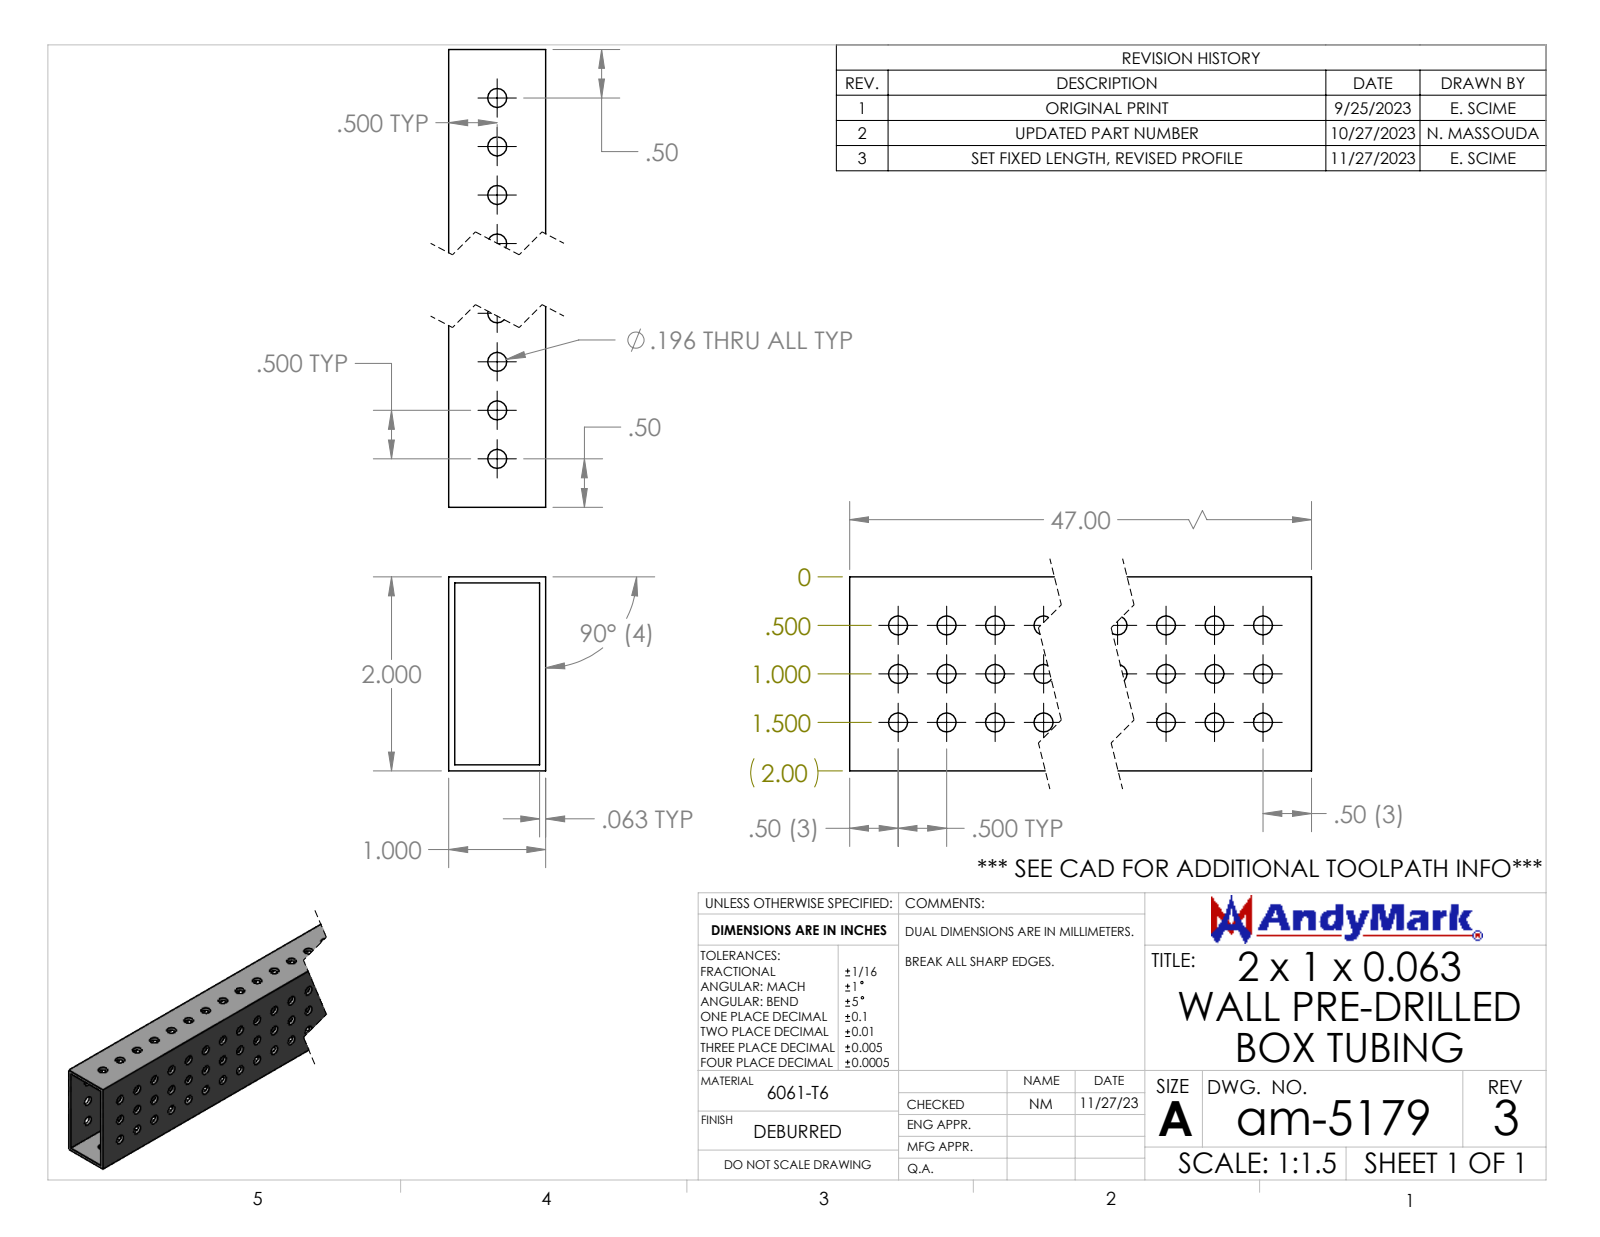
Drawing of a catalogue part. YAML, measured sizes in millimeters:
part_name: "am-5179 2x1x0.063 Wall Pre-Drilled Box Tube"
step_written_by: "SolidWorks 2024 (AUTOMOTIVE_DESIGN)"
units: millimeters
bodies: {solids: 1, faces: 1498, planar: 10, cylindrical: 1488, other: 0}
overall_size: [1193.8, 50.8, 25.4]
volume: 253800
surface_area: 338700
round_holes:
  - {diameter: 5, count: 372}
face_to_face_distances: [1.6, 23.8, 25.4, 22.2, 49.2, 50.8, 47.6, 1193.8]
hole_center_spacings: [12.7, 25.4, 38.1, 28.4, 50.8, 63.5, 76.2, 18]
